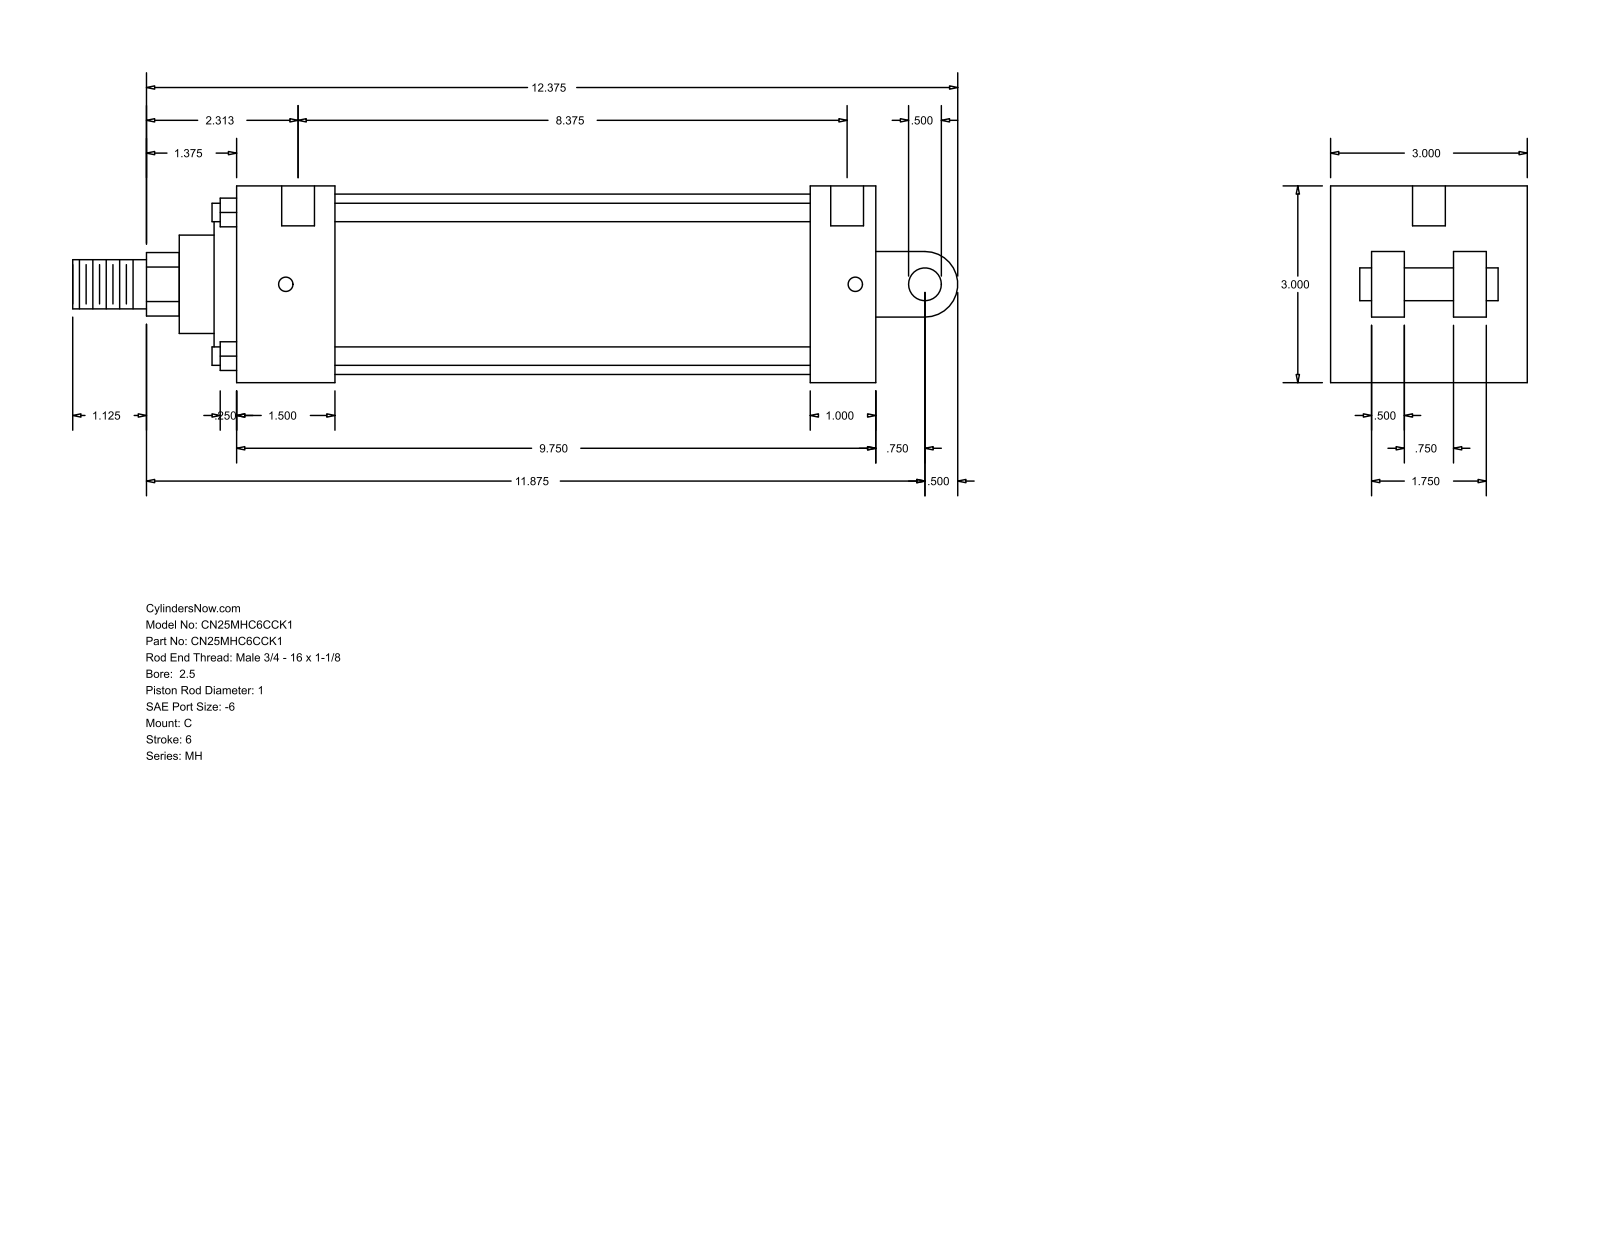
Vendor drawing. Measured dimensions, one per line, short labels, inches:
name: MH_C__0250_1
written by: GSSL Pune (CONFIG_CONTROL_DESIGN)
unit: in
bodies: 0 solids, 101 faces (71 planar, 30 cylindrical, 0 other)
size: 13.5 × 3 × 3
holes: 4× ⌀0.219, 2× ⌀0.5
bosses: 4× ⌀0.281, 1× ⌀2.75, 1× ⌀2.375, 1× ⌀1.5, 1× ⌀1, 1× ⌀0.75, 1× ⌀0.5
rounds: 1× R0.484, 1× R0.5
face distances: 3, 9.75, 1, 2.375, 0.625, 8.75, 1.5, 7.25, 8.25, 0.5
hole spacings: 8.687, 0.125, 0.187, 8.375, 8.5, 8.562
